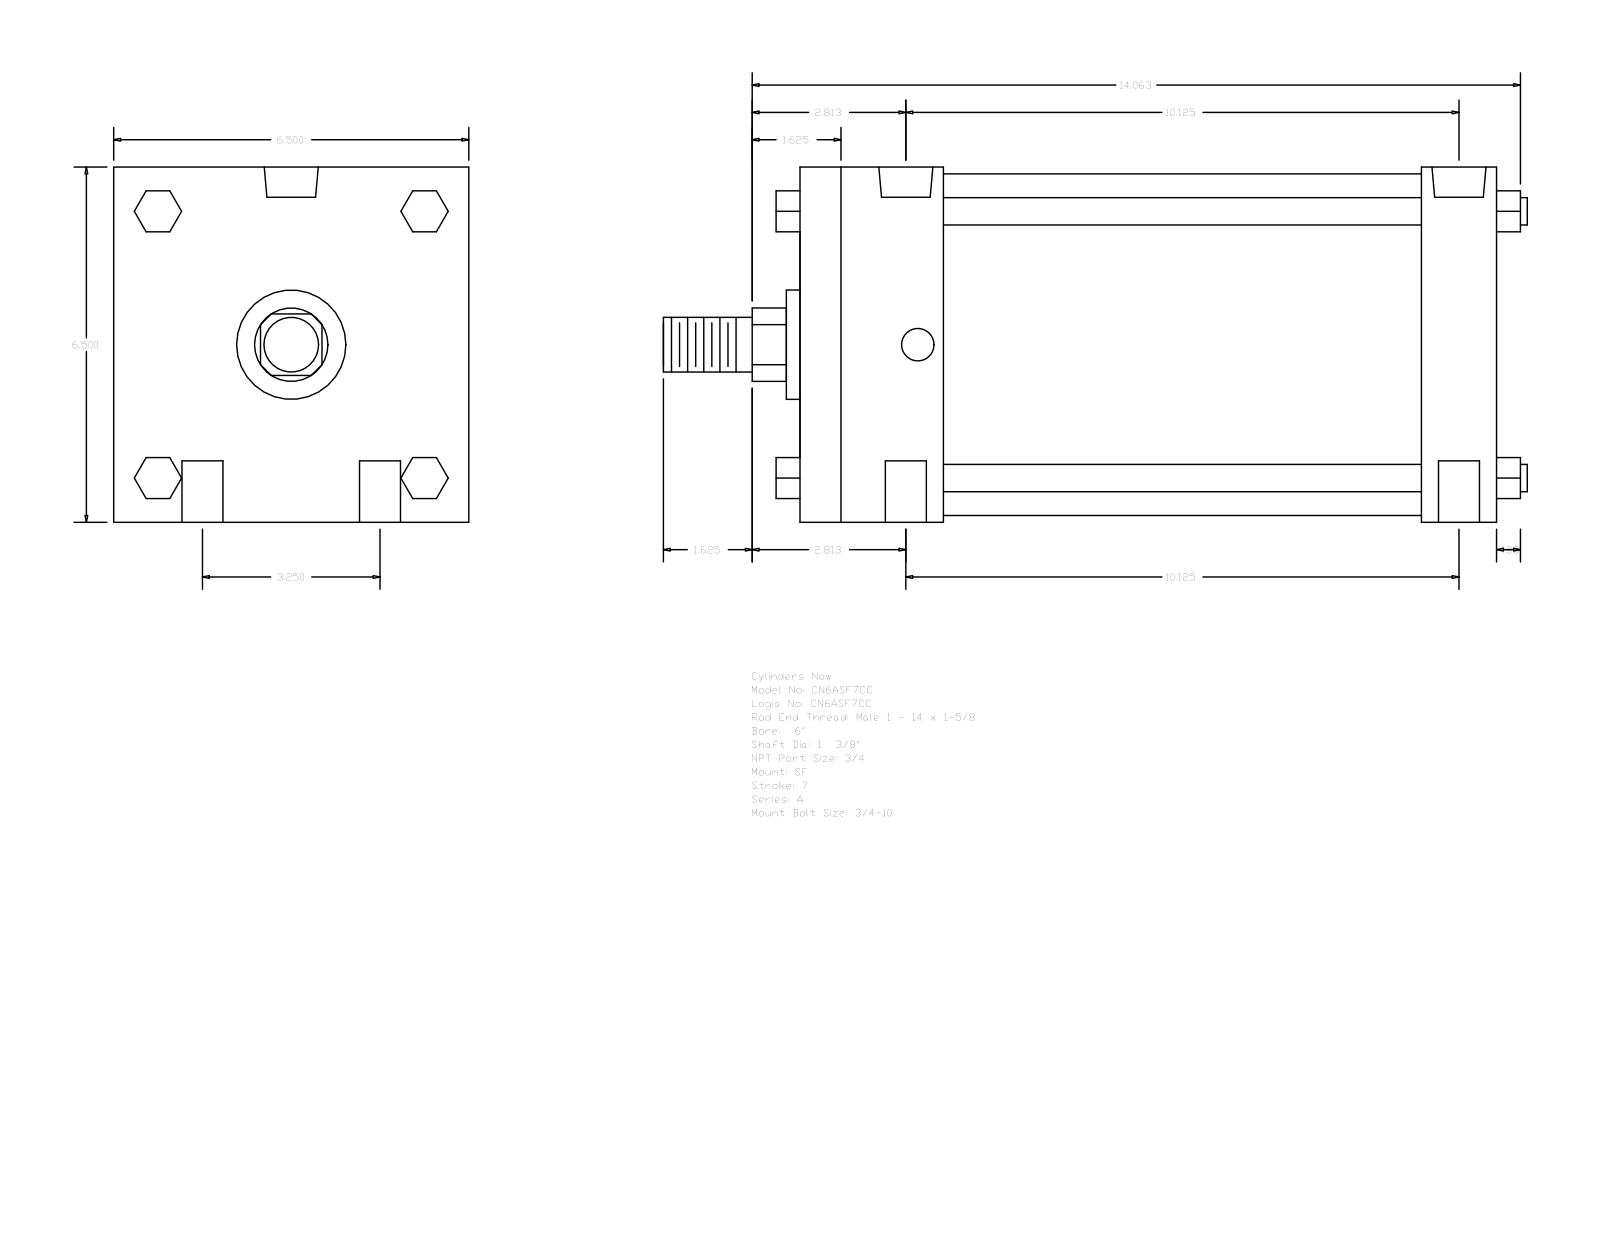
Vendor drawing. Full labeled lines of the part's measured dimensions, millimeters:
Part name (STEP PRODUCT): A_SF__0600_1.375
STEP written by: GSSL Pune (CONFIG_CONTROL_DESIGN)
Units: millimetres
Bodies: 0 solids, 124 faces (94 planar, 30 cylindrical, 0 other)
Overall size (bounding box): 401.64 × 165.1 × 165.1
Round holes (diameter × count): ⌀19.05 ×4, ⌀15.08 ×2, ⌀25.12 ×2
Round bosses / shafts (diameter × count): ⌀12.7 ×4, ⌀158.75 ×1, ⌀50.8 ×1, ⌀34.92 ×1, ⌀25.4 ×1
Partial cylindrical surfaces — rounded edges, fillets, slot ends (radius × count): R17.06 ×1
Main face-to-face distances: 165.1, 323.84, 288.92, 34.92, 66.67, 222.25, 257.17, 19.05, 61.97, 107.34
Hole centre spacings: 41.27, 260.46, 257.17, 82.54, 270.09, 246.05
